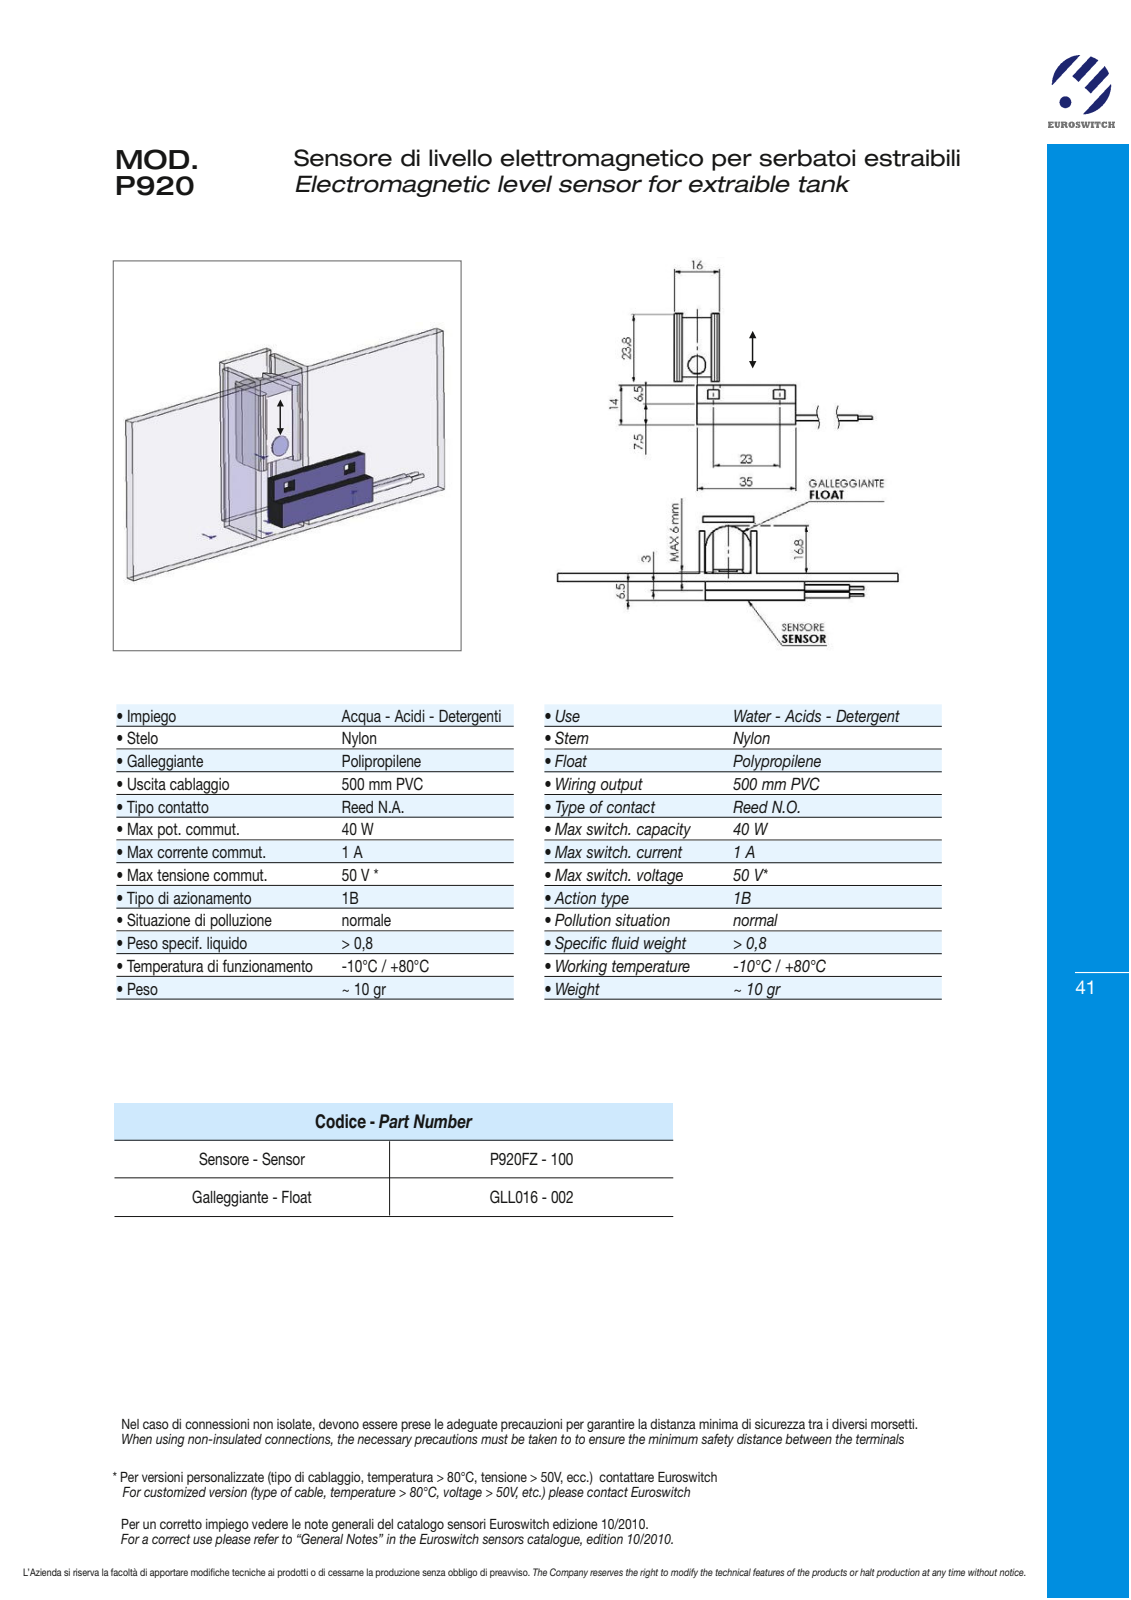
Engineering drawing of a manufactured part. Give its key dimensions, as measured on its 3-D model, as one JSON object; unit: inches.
{"part_name": "P920", "step_written_by": "SolidWorks 2019 (AUTOMOTIVE_DESIGN)", "units": "inches", "bodies": {"solids": 0, "faces": 195, "planar": 127, "cylindrical": 58, "other": 10}, "overall_size": [6.476, 1.146, 0.316], "round_bosses_or_shafts": [[0.059, 7], [0.22, 1]], "partial_cylinders_radius": [[0.016, 24], [0.024, 6], [0.02, 2]], "face_to_face_distances": [0.394, 0.034, 0.022, 0.337, 0.787, 0.358, 0.415, 0.73, 0.372, 0.057]}
